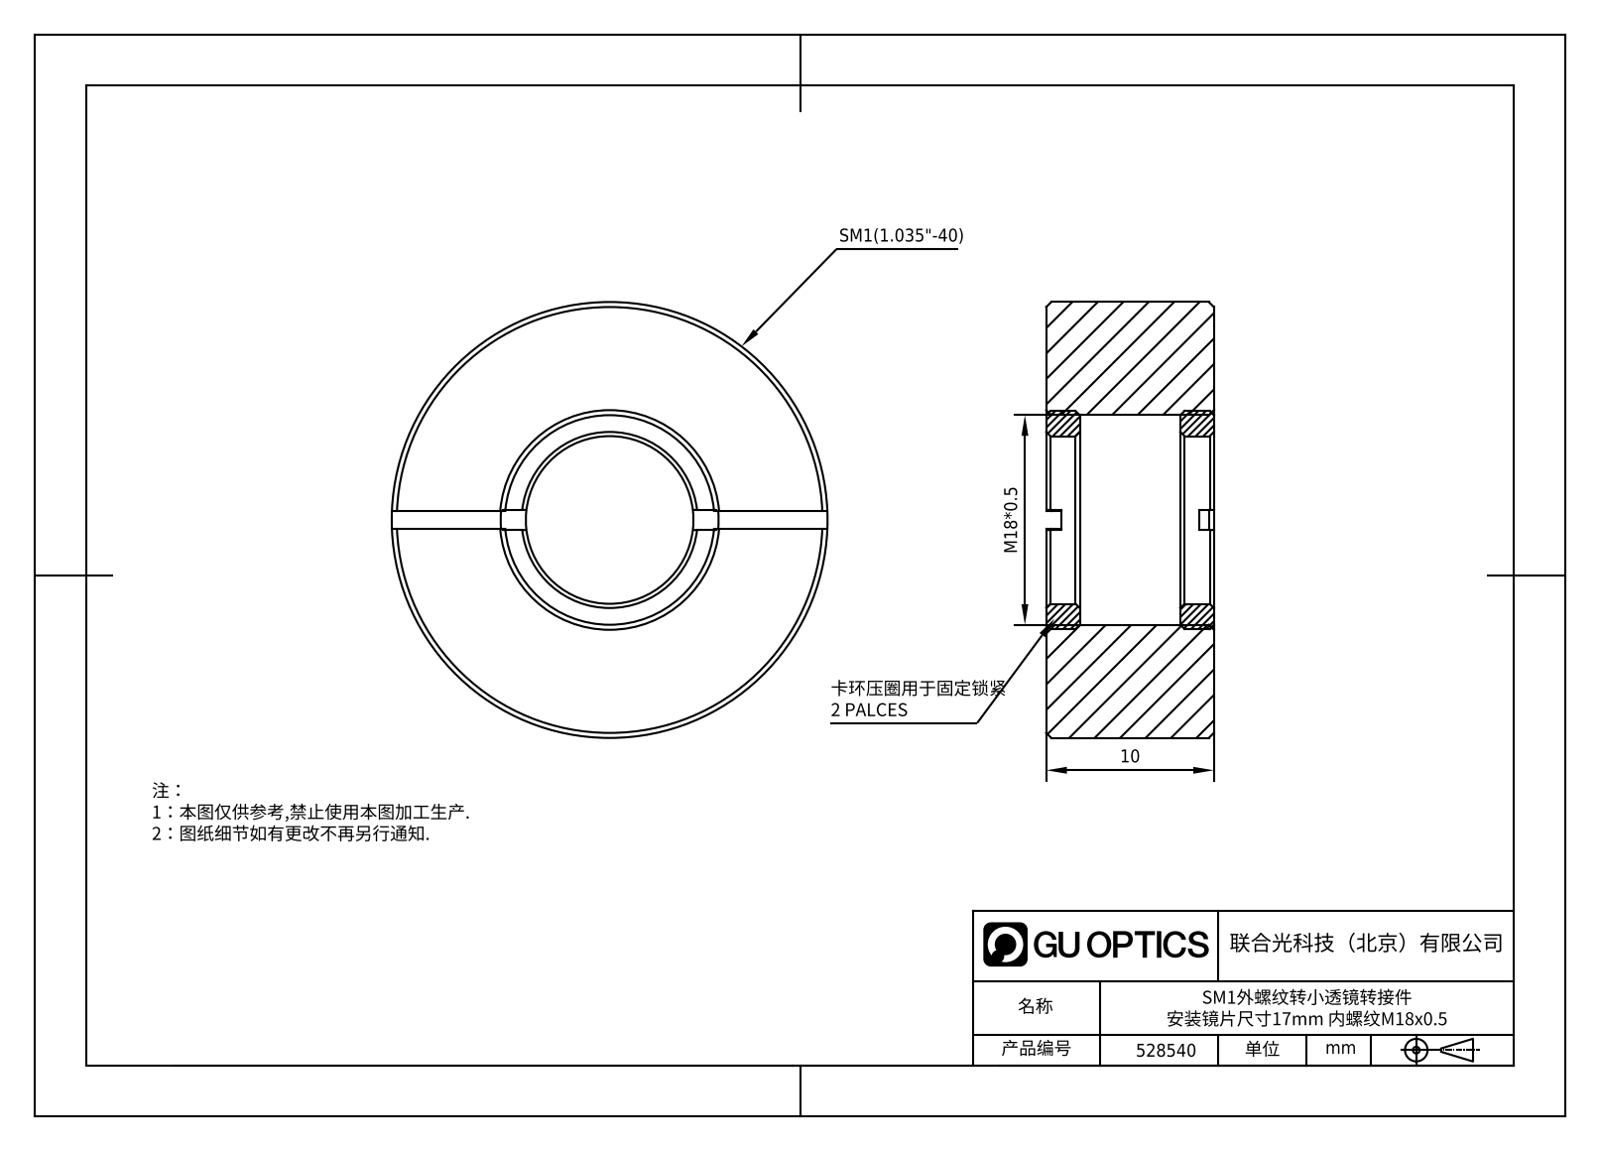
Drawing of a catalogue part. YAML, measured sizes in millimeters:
part_name: "528540"
step_written_by: "SolidWorks 2020 (CONFIG_CONTROL_DESIGN)"
units: millimeters
bodies: {solids: 3, faces: 51, planar: 27, cylindrical: 6, other: 18}
overall_size: [26, 26, 10]
volume: 3174
surface_area: 2580
round_holes:
  - {diameter: 15, count: 1}
  - {diameter: 17.5, count: 1}
round_bosses_or_shafts:
  - {diameter: 26, count: 1}
  - {diameter: 18, count: 1}
face_to_face_distances: [10, 2, 8, 6, 1, 1.1, 1.15, 9, 7, 0.9]
